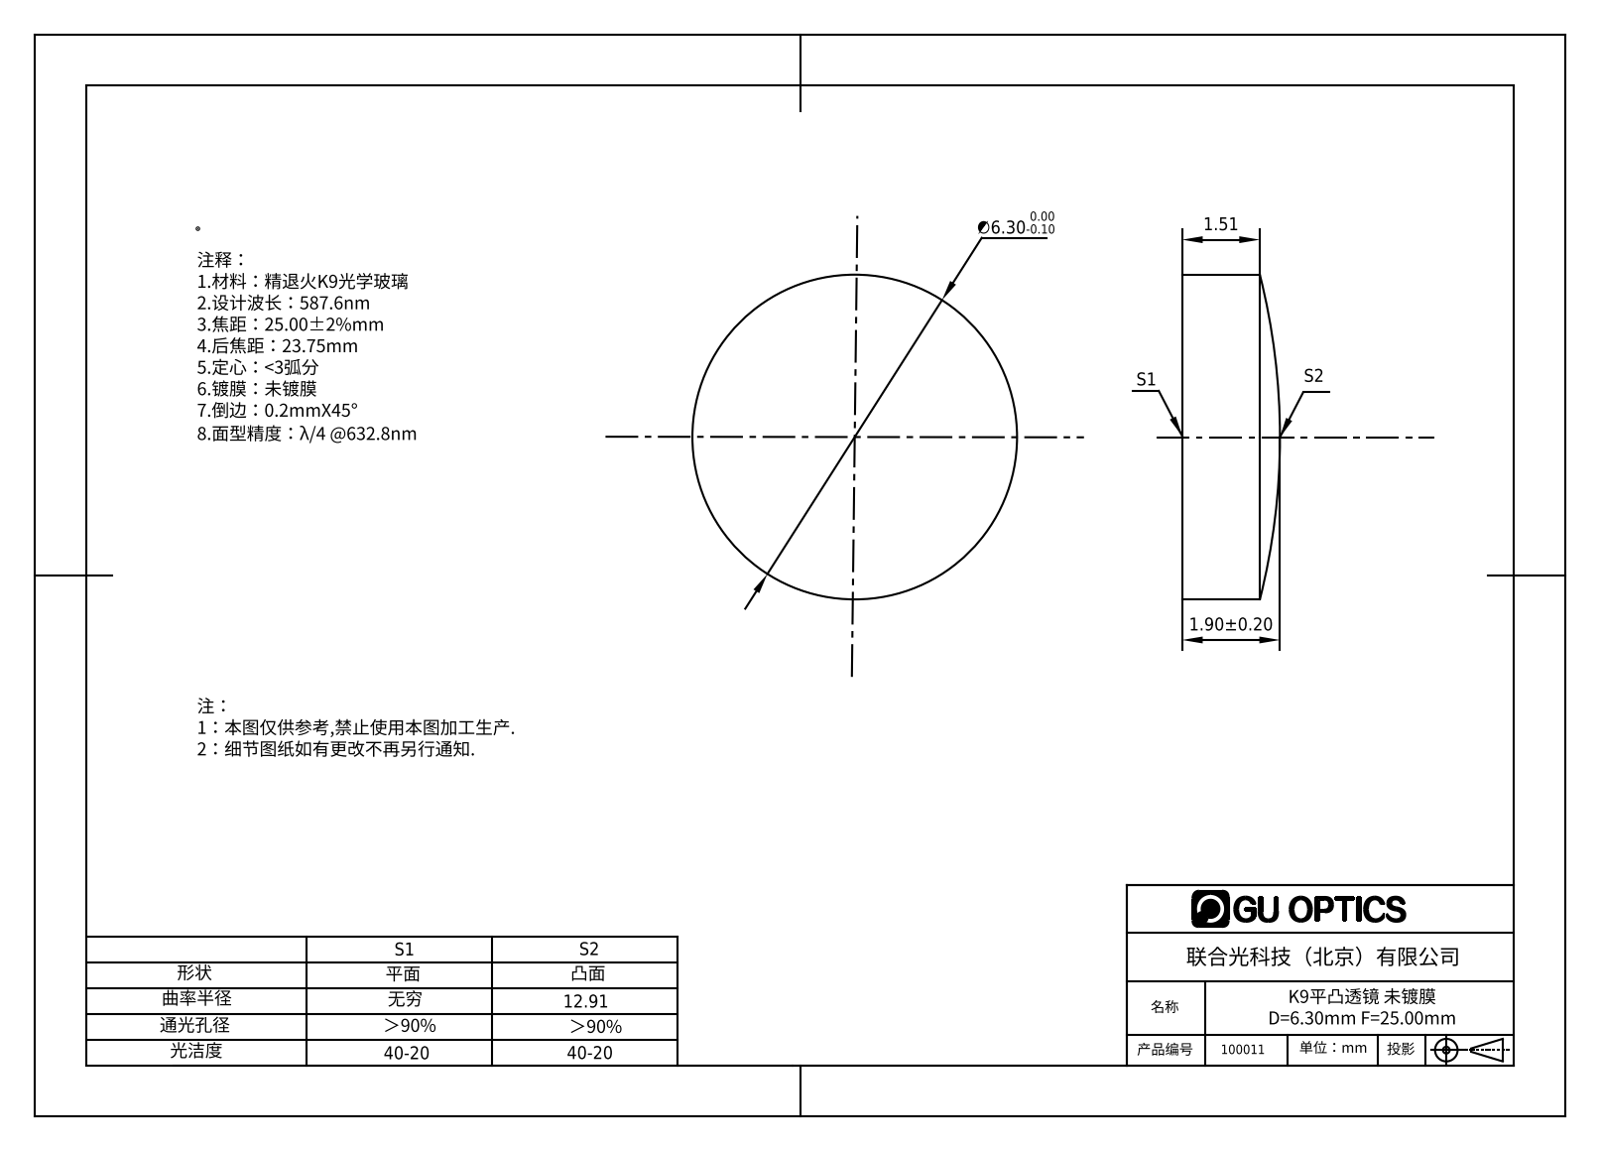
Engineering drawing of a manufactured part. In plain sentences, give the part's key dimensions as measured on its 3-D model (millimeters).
The part is named "100011". Its 3-D file was written by "SolidWorks 2016 (AUTOMOTIVE_DESIGN)". It is 1 solid with 5 faces: 1 planar, 2 cylindrical and 2 other. Overall it measures 6.3 by 6.3 by 1.9 millimeters. Its volume is 53 cubic millimeters and its surface area 93 square millimeters. Round bosses or shafts: 1 of diameter 6.3.
